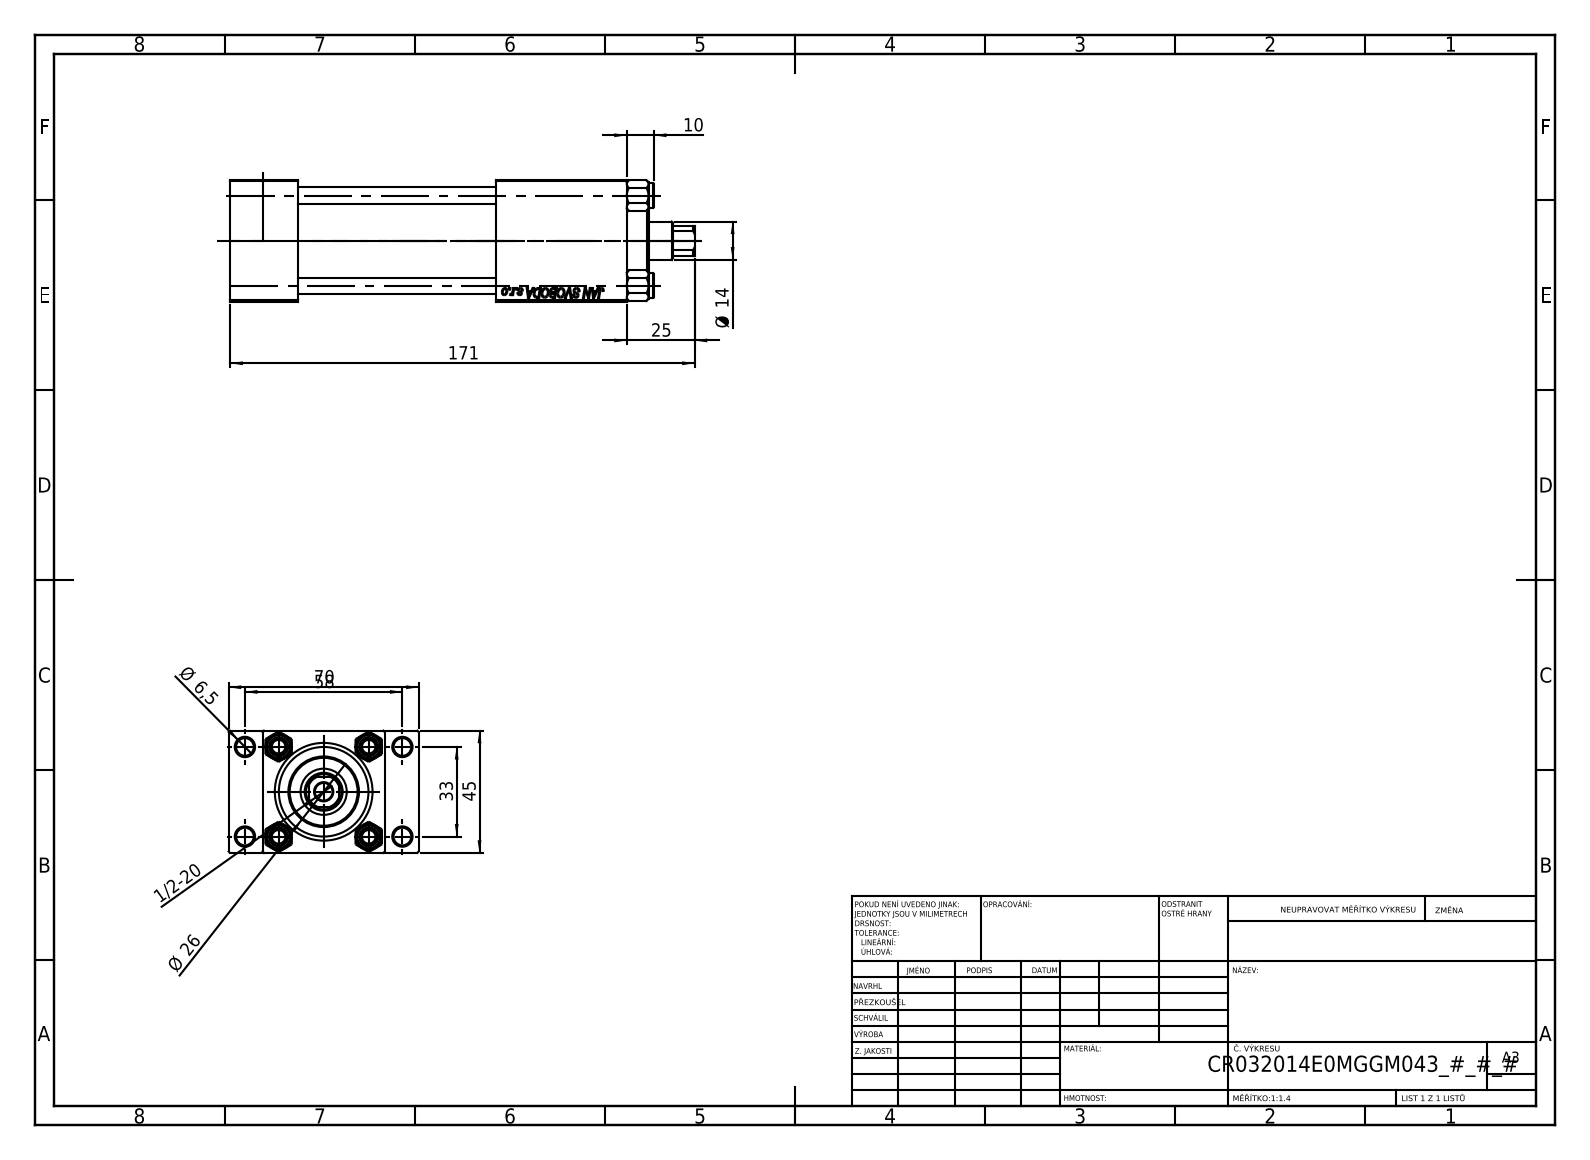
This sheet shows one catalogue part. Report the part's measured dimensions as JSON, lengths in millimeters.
{"part_name": "V215CR_VCP_E; NUT_M5_E; V215CR_E_Body; V215CR_TYCINKA_E (+1 more)", "step_written_by": "SolidWorks 2019 (CONFIG_CONTROL_DESIGN)", "units": "millimeters", "bodies": {"solids": 11, "faces": 1136, "planar": 497, "cylindrical": 87, "other": 552}, "overall_size": [171, 70, 45], "volume_mm3": 233802, "surface_area_mm2": 83877, "round_holes": [[6.5, 5], [6, 4], [7, 2], [13.16, 2], [20, 2], [14, 1], [17, 1], [24, 1], [32, 1], [33, 1]], "round_bosses_or_shafts": [[9, 4], [38, 1], [26, 1]], "partial_cylinders_radius": [[6.5, 1]], "face_to_face_distances": [45, 25, 12.5, 57.5, 146, 121, 73, 70, 98, 48], "hole_center_spacings": [12.4, 23.48, 33.2, 33.37, 35.35, 45.6, 56.35, 33]}
